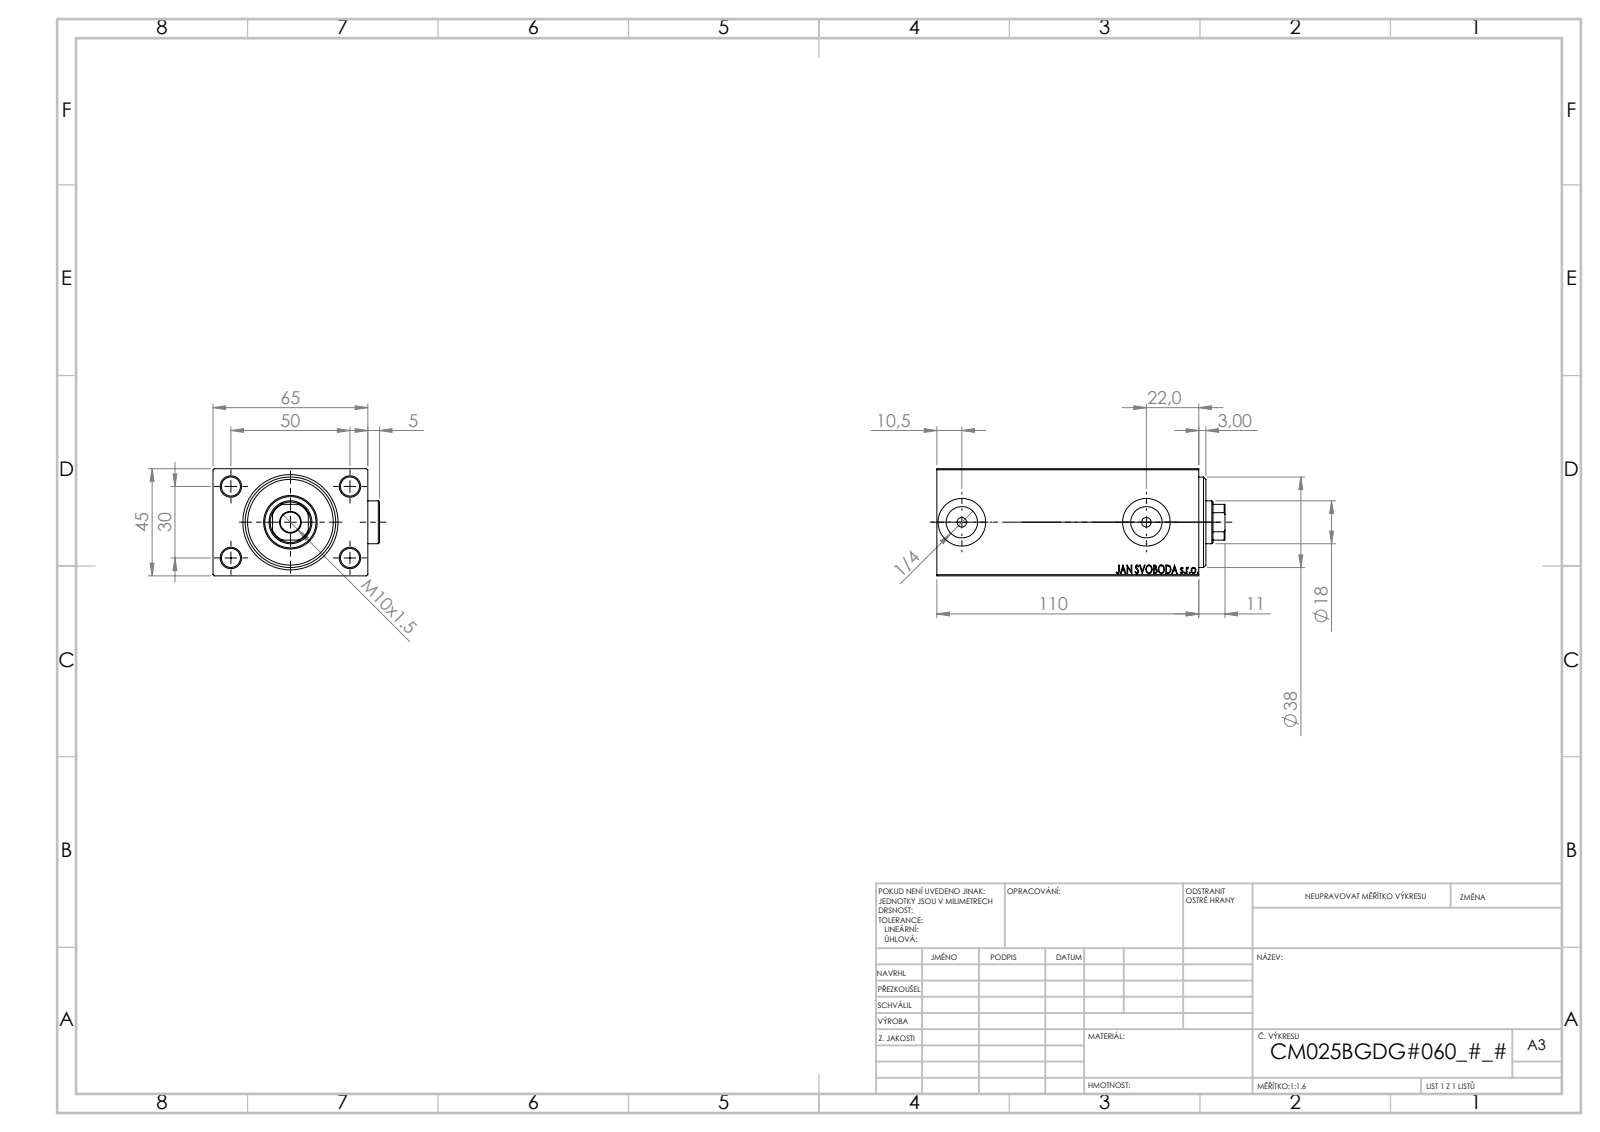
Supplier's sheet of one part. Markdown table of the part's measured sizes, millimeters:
| quantity | value |
| --- | --- |
| part name | Zatka_OIL_PORT; V450CM_B_Body; V450CM_B_VCP; V450CM_VC_B |
| STEP written by | SolidWorks 2019 (CONFIG_CONTROL_DESIGN) |
| units | millimeters |
| bodies | 5 solids, 935 faces (435 planar, 70 cylindrical, 430 other) |
| overall size | 121 × 69.9 × 45 |
| volume | 299 869 mm³ |
| surface area | 58 065 mm² |
| round holes (diameter × count) | 8 × 4, 4 × 2, 13.16 × 2, 20 × 2, 8.5 × 1, 18 × 1, 21.5 × 1, 22.5 × 1, 25 × 1, 27 × 1, 38 × 1 |
| round bosses / shafts (diameter × count) | 18 × 2 |
| partial cylindrical surfaces (radius × count) | 8.5 × 1 |
| main face-to-face distances | 45, 65, 5, 6, 110, 99, 64.9, 105, 104, 8 |
| hole center spacings | 29.15, 30, 50, 58.31, 77.5 |
